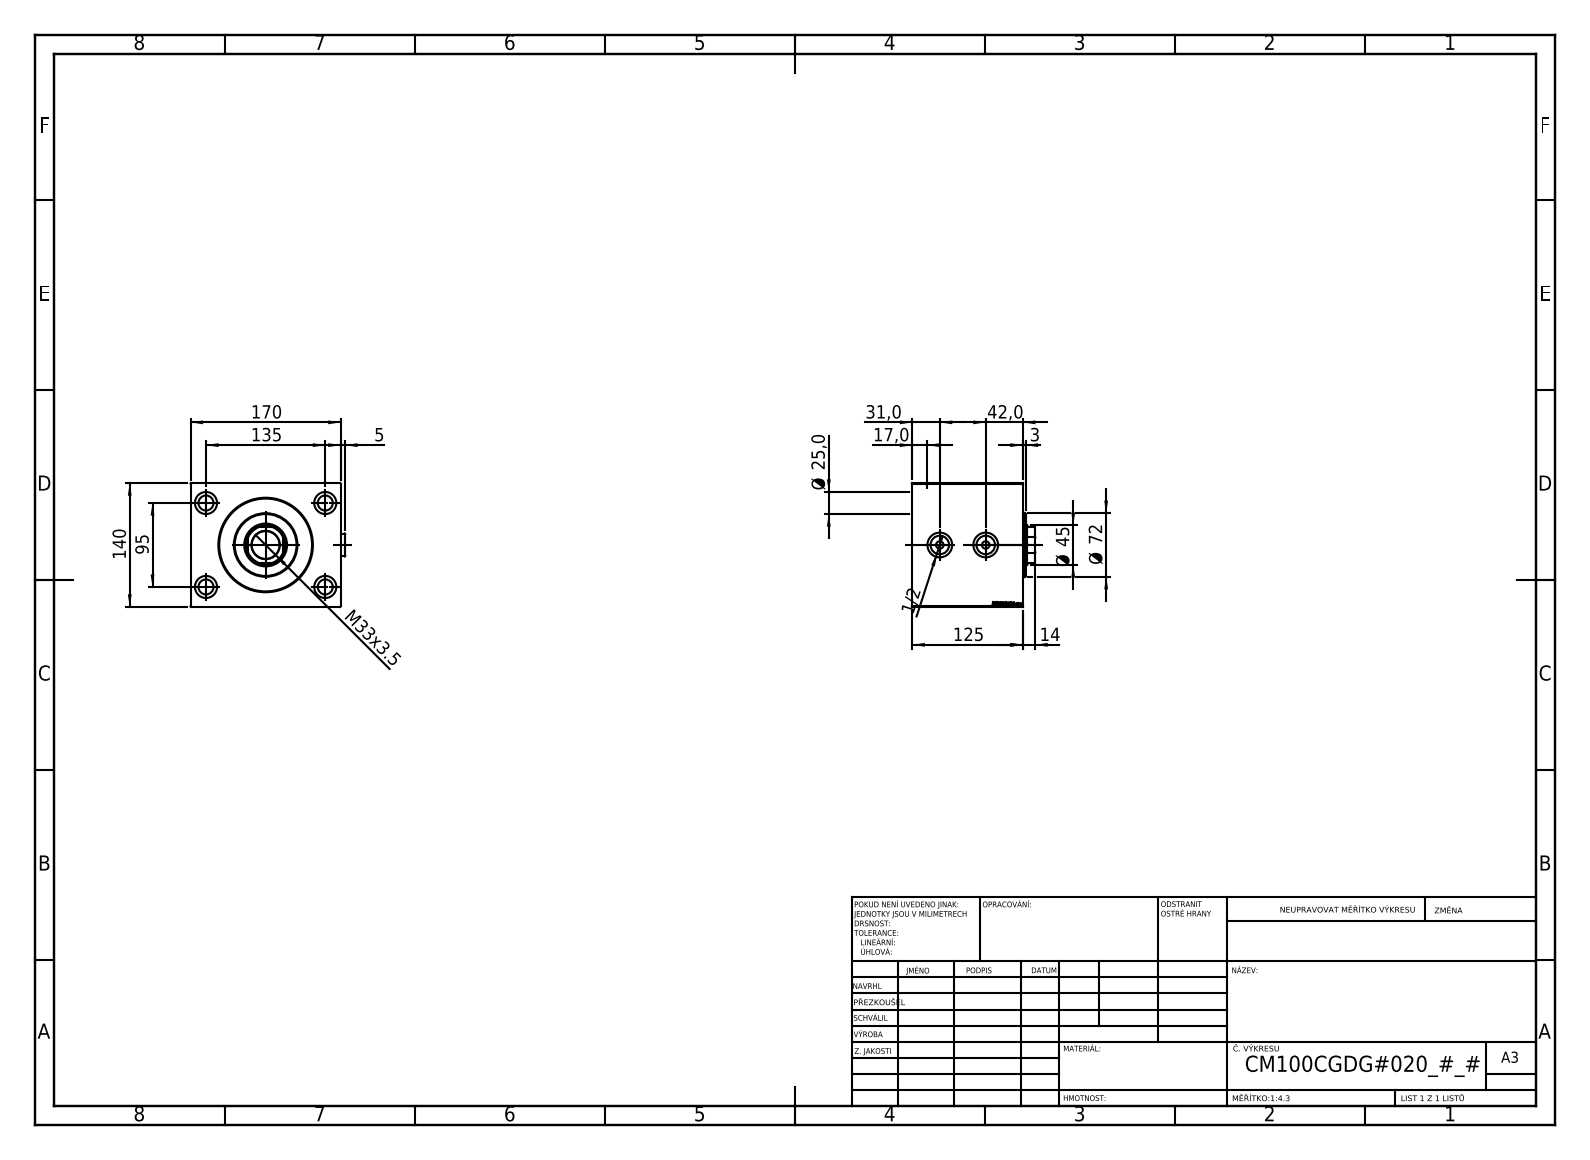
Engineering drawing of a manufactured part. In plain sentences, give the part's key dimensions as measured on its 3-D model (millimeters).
The part is named "V450CM_C_VCP; V450CM_C_Body; Zatka_OIL_PORT; V450CM_VC_B". Its 3-D file was written by "SolidWorks 2019 (CONFIG_CONTROL_DESIGN)". It is 5 solids with 917 faces: 443 planar, 76 cylindrical and 398 other. Overall it measures 174.9 by 140 by 139 millimeters. Its volume is 2 734 000 cubic millimeters and its surface area 237 780 square millimeters. Round holes: 4 of diameter 17, 4 of diameter 25, 2 of diameter 8.5, 2 of diameter 20.96, 2 of diameter 28, 1 of diameter 31.5, 1 of diameter 45, 1 of diameter 48.5, 1 of diameter 100, 1 of diameter 102, 1 of diameter 105. Round bosses or shafts: 2 of diameter 26, 1 of diameter 72. Partial cylindrical surfaces (rounded edges, fillets, slot ends): 1 of radius 22. The main face-to-face distances are 140, 125, 170, 51, 74, 21.6, 29.4, 103.4, 10, 31.6. The hole center spacings are 82.54, 95, 135, 165.08, 52.
